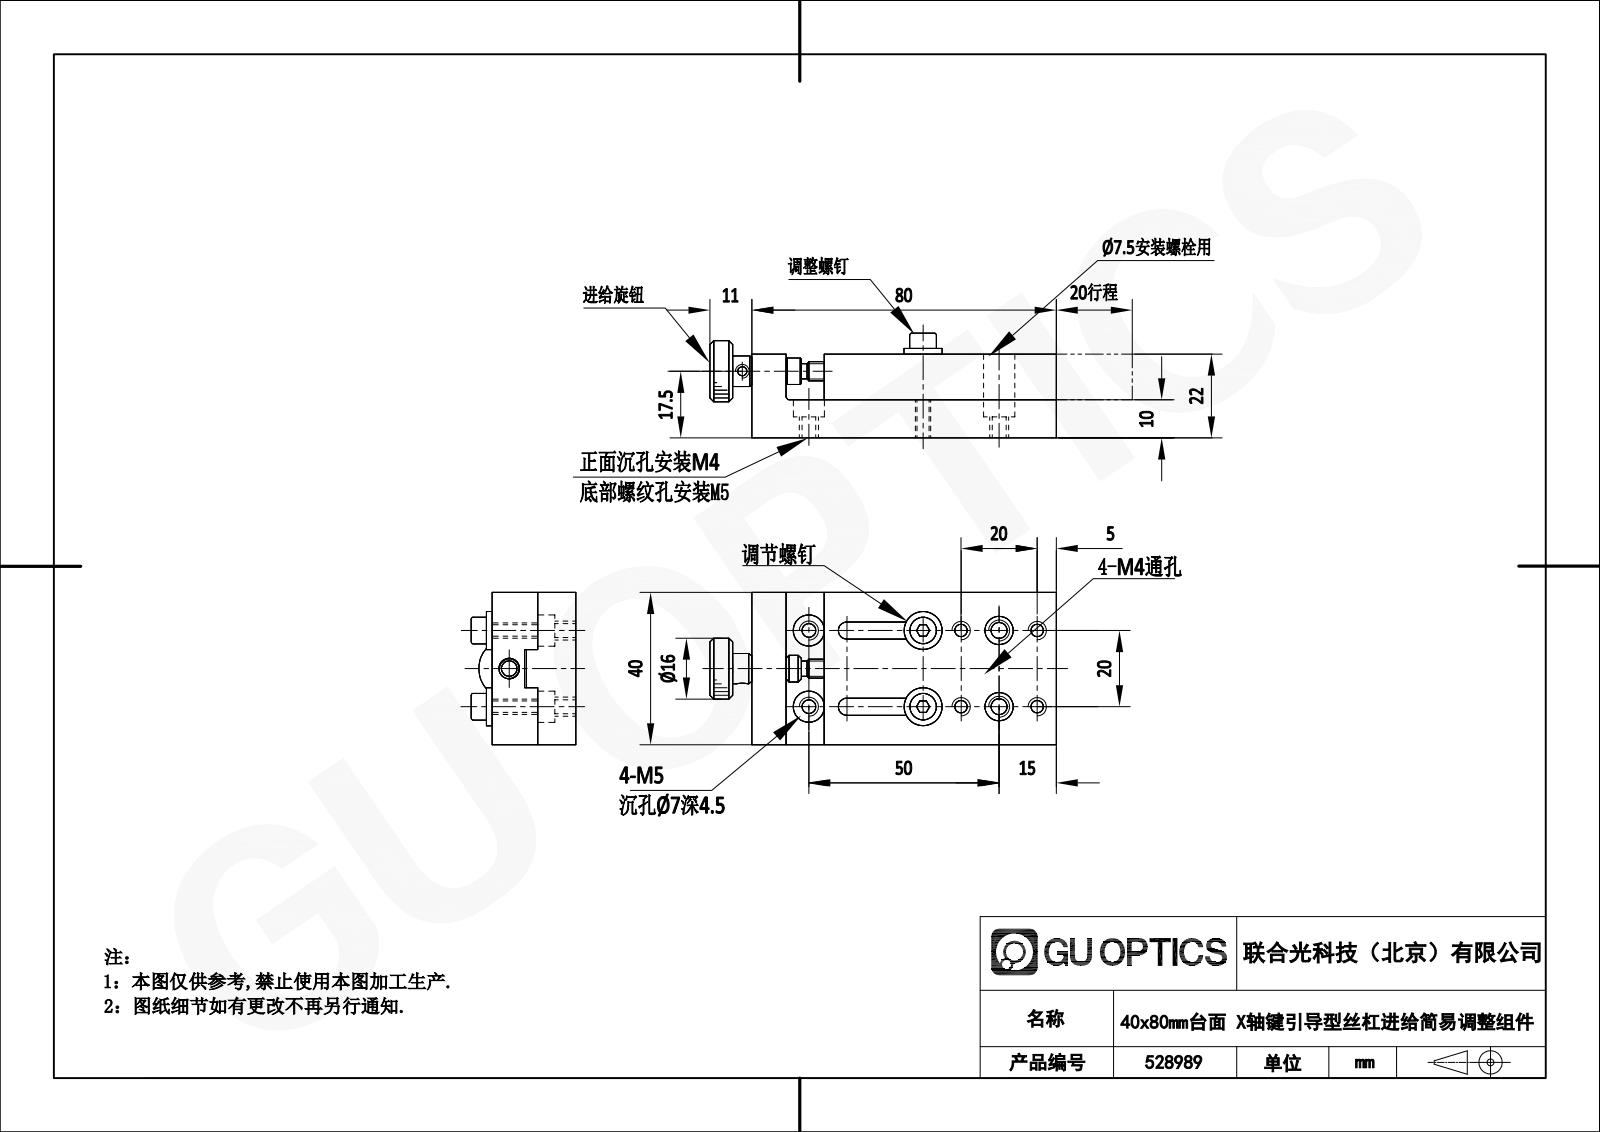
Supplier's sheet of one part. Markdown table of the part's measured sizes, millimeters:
| quantity | value |
| --- | --- |
| part name | 528991 |
| STEP written by | SolidWorks 2020 (CONFIG_CONTROL_DESIGN) |
| units | millimeters |
| bodies | 5 solids, 271 faces (120 planar, 66 cylindrical, 85 other) |
| overall size | 91 × 40 × 27.5 |
| volume | 61 434 mm³ |
| surface area | 23 972 mm² |
| round holes (diameter × count) | 3.24 × 6, 4.13 × 5, 7.5 × 4, 2.46 × 1, 4.5 × 1, 5.5 × 1 |
| round bosses / shafts (diameter × count) | 7 × 3, 4 × 3, 10 × 2, 8 × 1, 5 × 1 |
| partial cylindrical surfaces (radius × count) | 2.25 × 4, 1 × 1, 8 × 1 |
| main face-to-face distances | 10, 22, 12, 40, 9, 80, 25, 15, 20, 13.5 |
| hole center spacings | 20, 10, 22.36, 28.28, 30, 36.06, 40, 44.72 |
